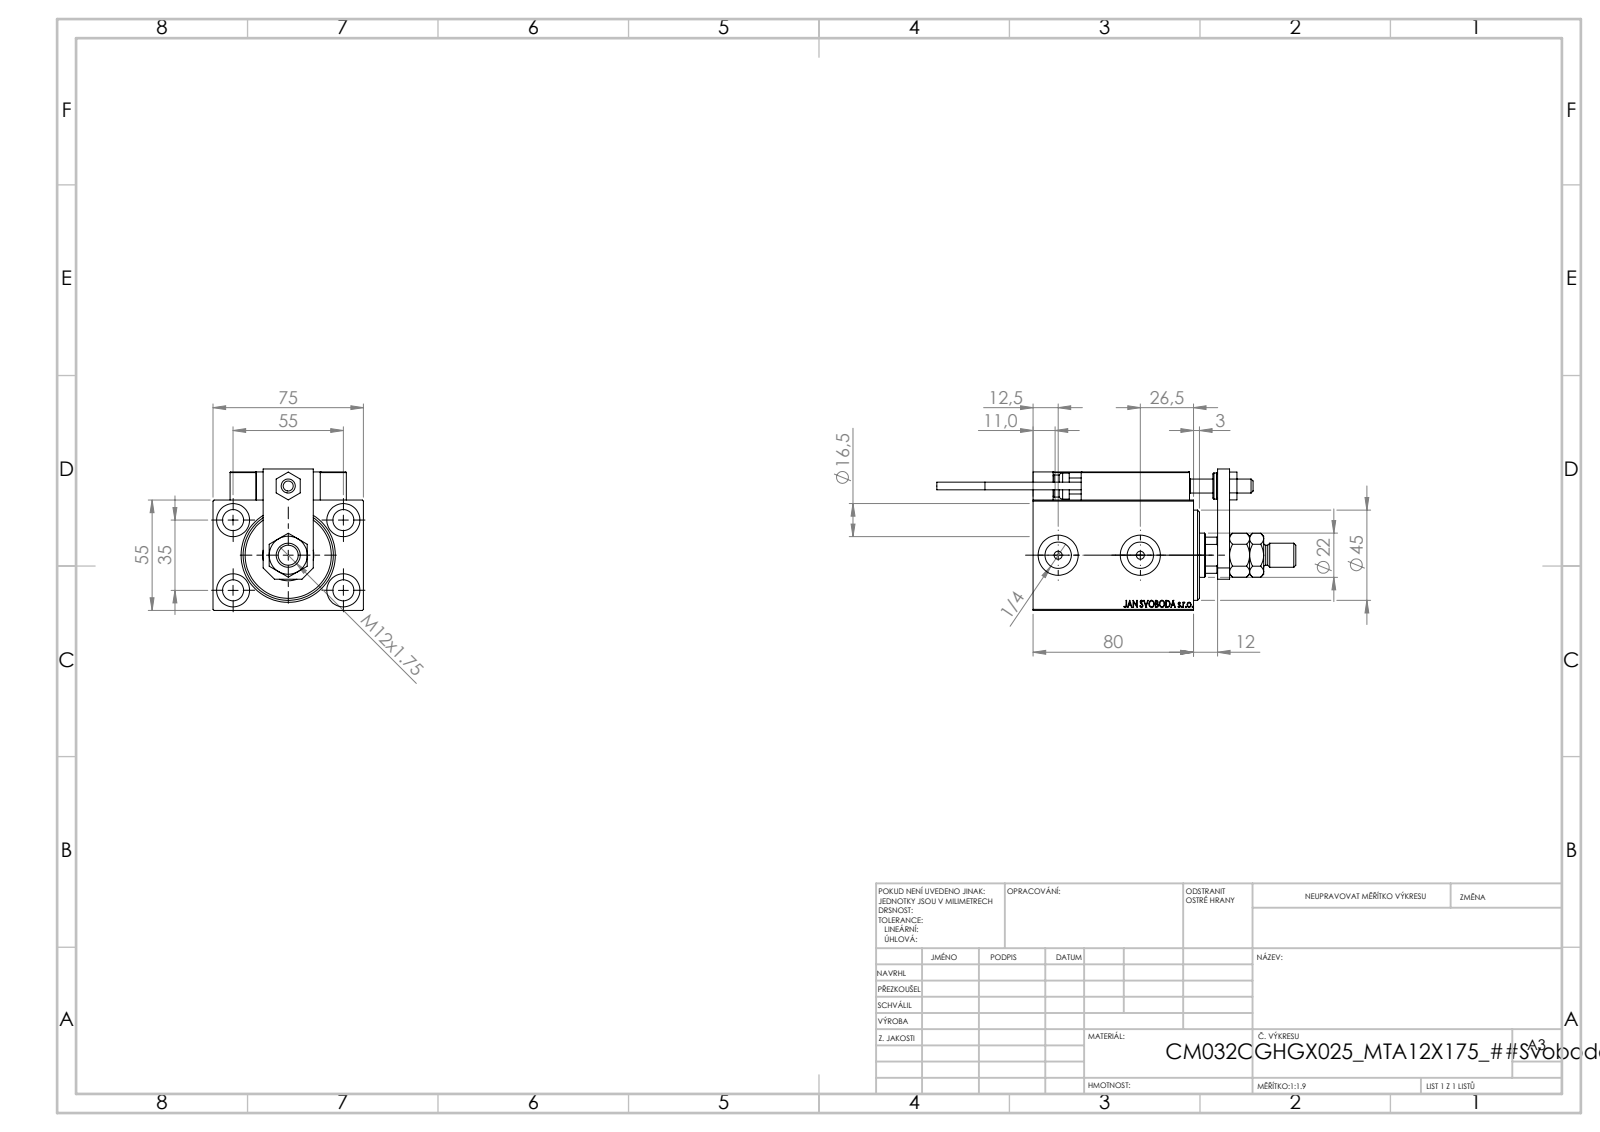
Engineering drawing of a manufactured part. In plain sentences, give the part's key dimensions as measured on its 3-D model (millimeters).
The part is named "V450CM_C_Body; Block; SWITCH DIM B,W; V450CM_VC_B (+7 more)". Its 3-D file was written by "SolidWorks 2019 (CONFIG_CONTROL_DESIGN)". It is 24 solids with 1331 faces: 575 planar, 192 cylindrical and 564 other. Overall it measures 179 by 75 by 70.5 millimeters. Its volume is 337 205 cubic millimeters and its surface area 89 744 square millimeters. Round holes: 6 of diameter 4, 5 of diameter 8, 5 of diameter 10.5, 5 of diameter 16.5, 4 of diameter 3.2, 2 of diameter 5, 2 of diameter 13.16, 2 of diameter 20, 1 of diameter 7, 1 of diameter 22, 1 of diameter 25.5, 1 of diameter 32. Round bosses or shafts: 2 of diameter 5, 2 of diameter 3.8, 1 of diameter 13, 1 of diameter 12, 1 of diameter 11, 1 of diameter 10. Partial cylindrical surfaces (rounded edges, fillets, slot ends): 30 of radius 0.3, 2 of radius 3, 1 of radius 10.5. The main face-to-face distances are 55, 75, 14, 69, 10, 12, 58, 25, 15, 7. The hole center spacings are 32.6, 11.37, 20, 29.59, 29.69, 32.06, 32.33, 35.
